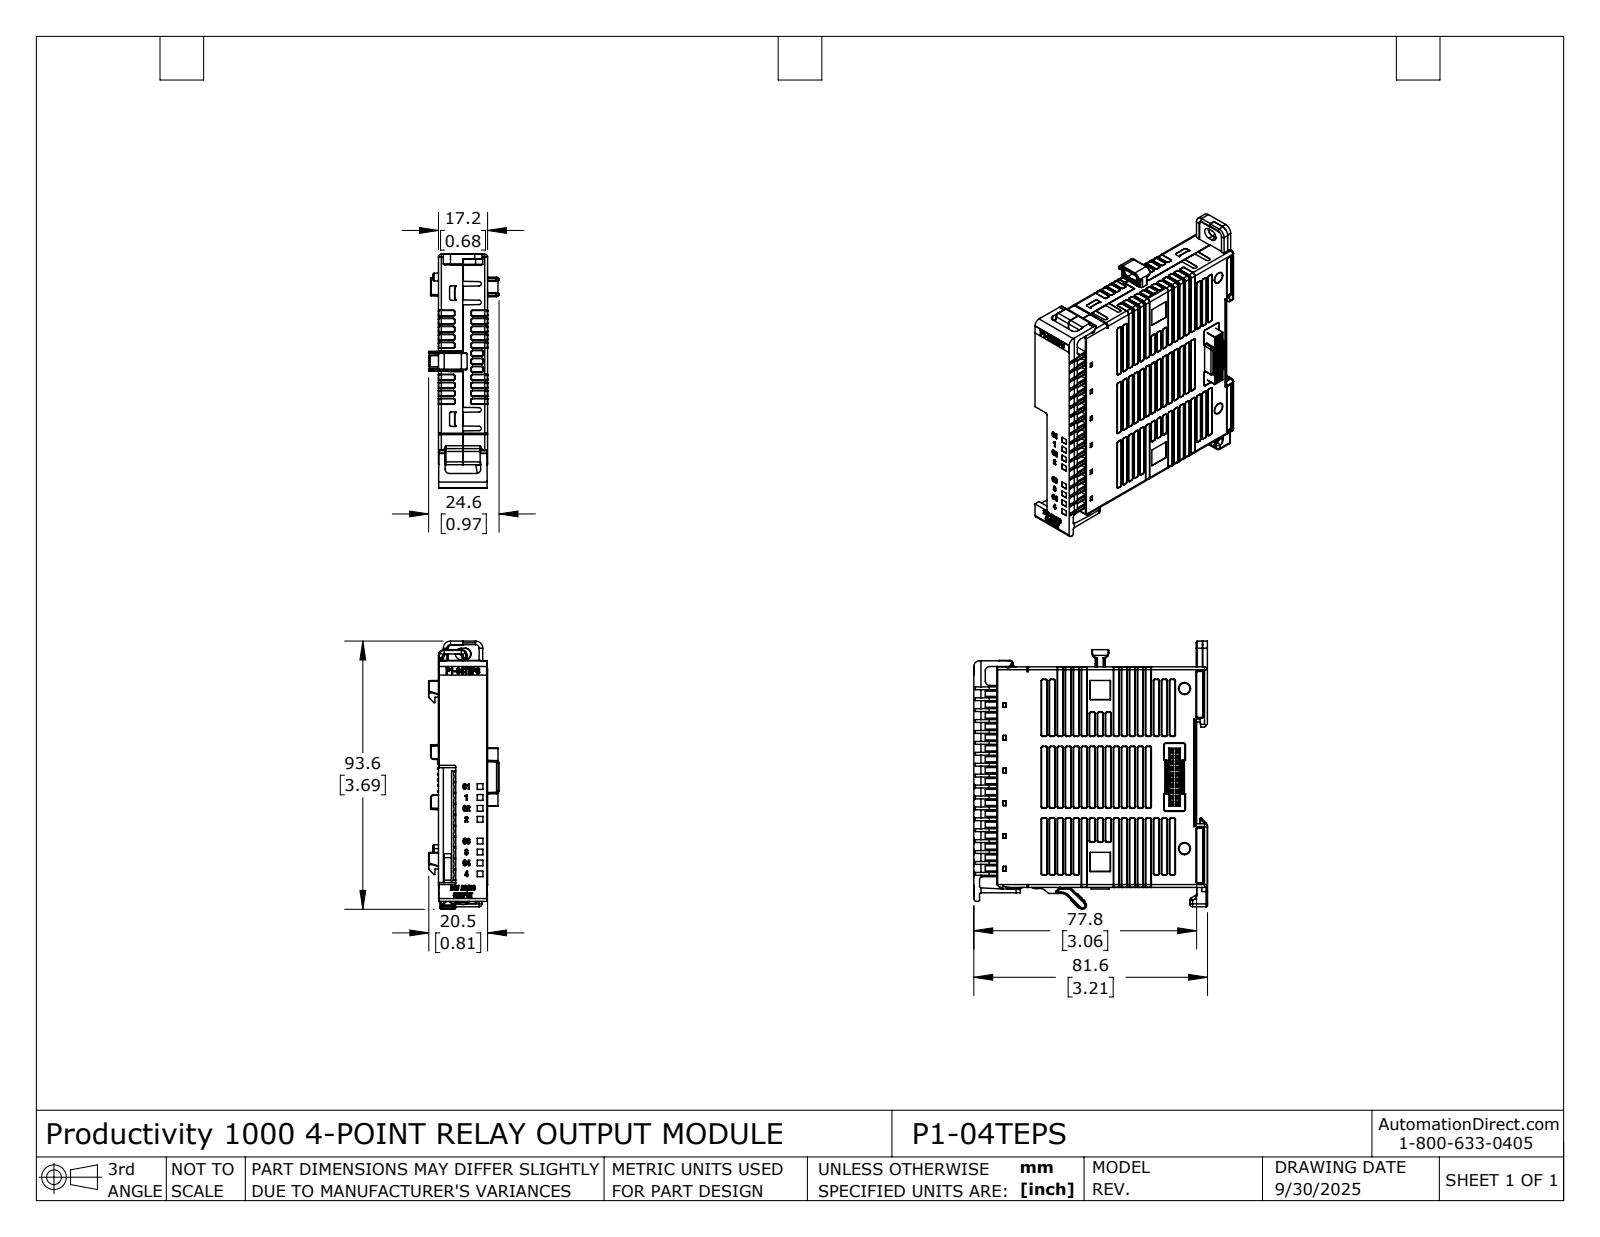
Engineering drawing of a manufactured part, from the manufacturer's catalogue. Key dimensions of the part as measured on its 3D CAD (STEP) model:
Part name (STEP PRODUCT): P1-04TEPS
STEP written by: SolidWorks 2024 (AUTOMOTIVE_DESIGN)
Units: inches
Bodies: 18 solids, 4347 faces (2321 planar, 1031 cylindrical, 995 other)
Overall size (bounding box): 3.686 × 3.214 × 0.969
Volume: 5.539 in³ · Surface area: 45.69 in²
Round holes (diameter × count): ⌀0.01 ×20, ⌀0.024 ×8, ⌀0.049 ×1
Round bosses / shafts (diameter × count): ⌀0.043 ×2
Partial cylindrical surfaces — rounded edges, fillets, slot ends (radius × count): R0.01 ×207, R0.02 ×135, R0.039 ×58, R0.079 ×12, R0.059 ×10, R0.059 ×9, R0.008 ×8, R0.03 ×8
Main face-to-face distances: 0.674, 0.675, 0.079, 0.672, 0.317, 3.064, 2.746, 0.071, 0.157, 0.065
Hole centre spacings: 0.079, 0.157, 0.176, 0.236, 0.315, 0.394, 0.402, 0.111
